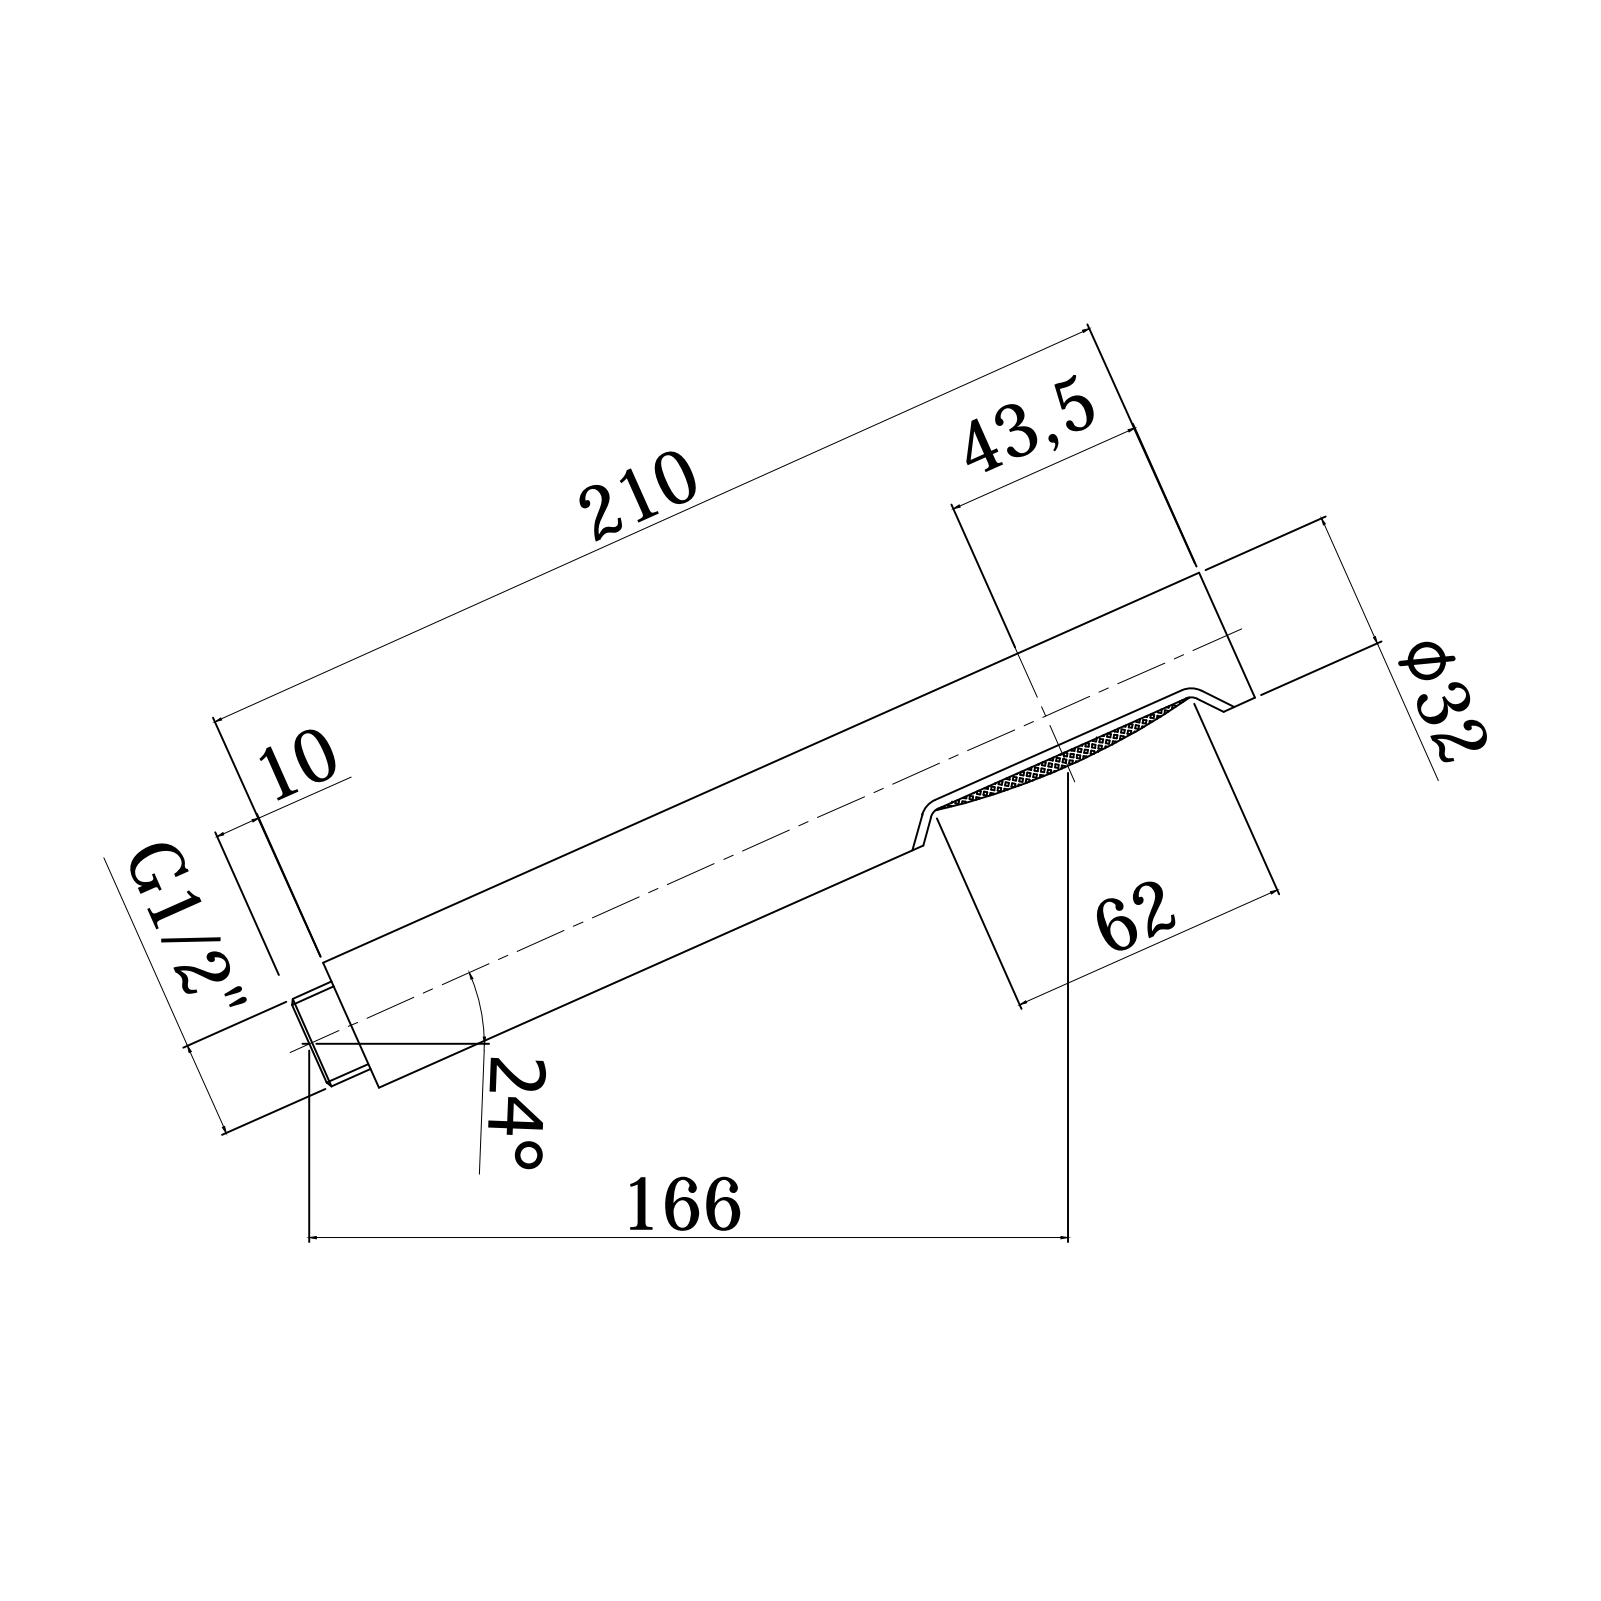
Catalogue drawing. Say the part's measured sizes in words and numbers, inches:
The part is named "ZDOC032CR". Its 3-D file was written by "CREO PARAMETRIC BY PTC INC, 2020044 (CONFIG_CONTROL_DESIGN)". It is 2 solids with 117 faces: 9 planar, 105 cylindrical and 3 other. Overall it measures 8.661 by 1.26 by 1.26 inches. Its volume is 3.218 cubic inches and its surface area 68.73 square inches. Round holes: 45 of diameter 0.059, 1 of diameter 1.102. Round bosses or shafts: 1 of diameter 1.26, 1 of diameter 1.087, 1 of diameter 0.827. Partial cylindrical surfaces (rounded edges, fillets, slot ends): 2 of radius 0.307, 2 of radius 0.386, 2 of radius 0.394, 1 of radius 0.63. The main face-to-face distances are 0.394, 0.079, 7.795, 7.874, 8.189, 8.268, 0.787, 8.583, 8.661. The hole center spacings are 0.311, 0.542, 0.788, 0.256, 1.039, 0.512, 0.177, 0.437.
